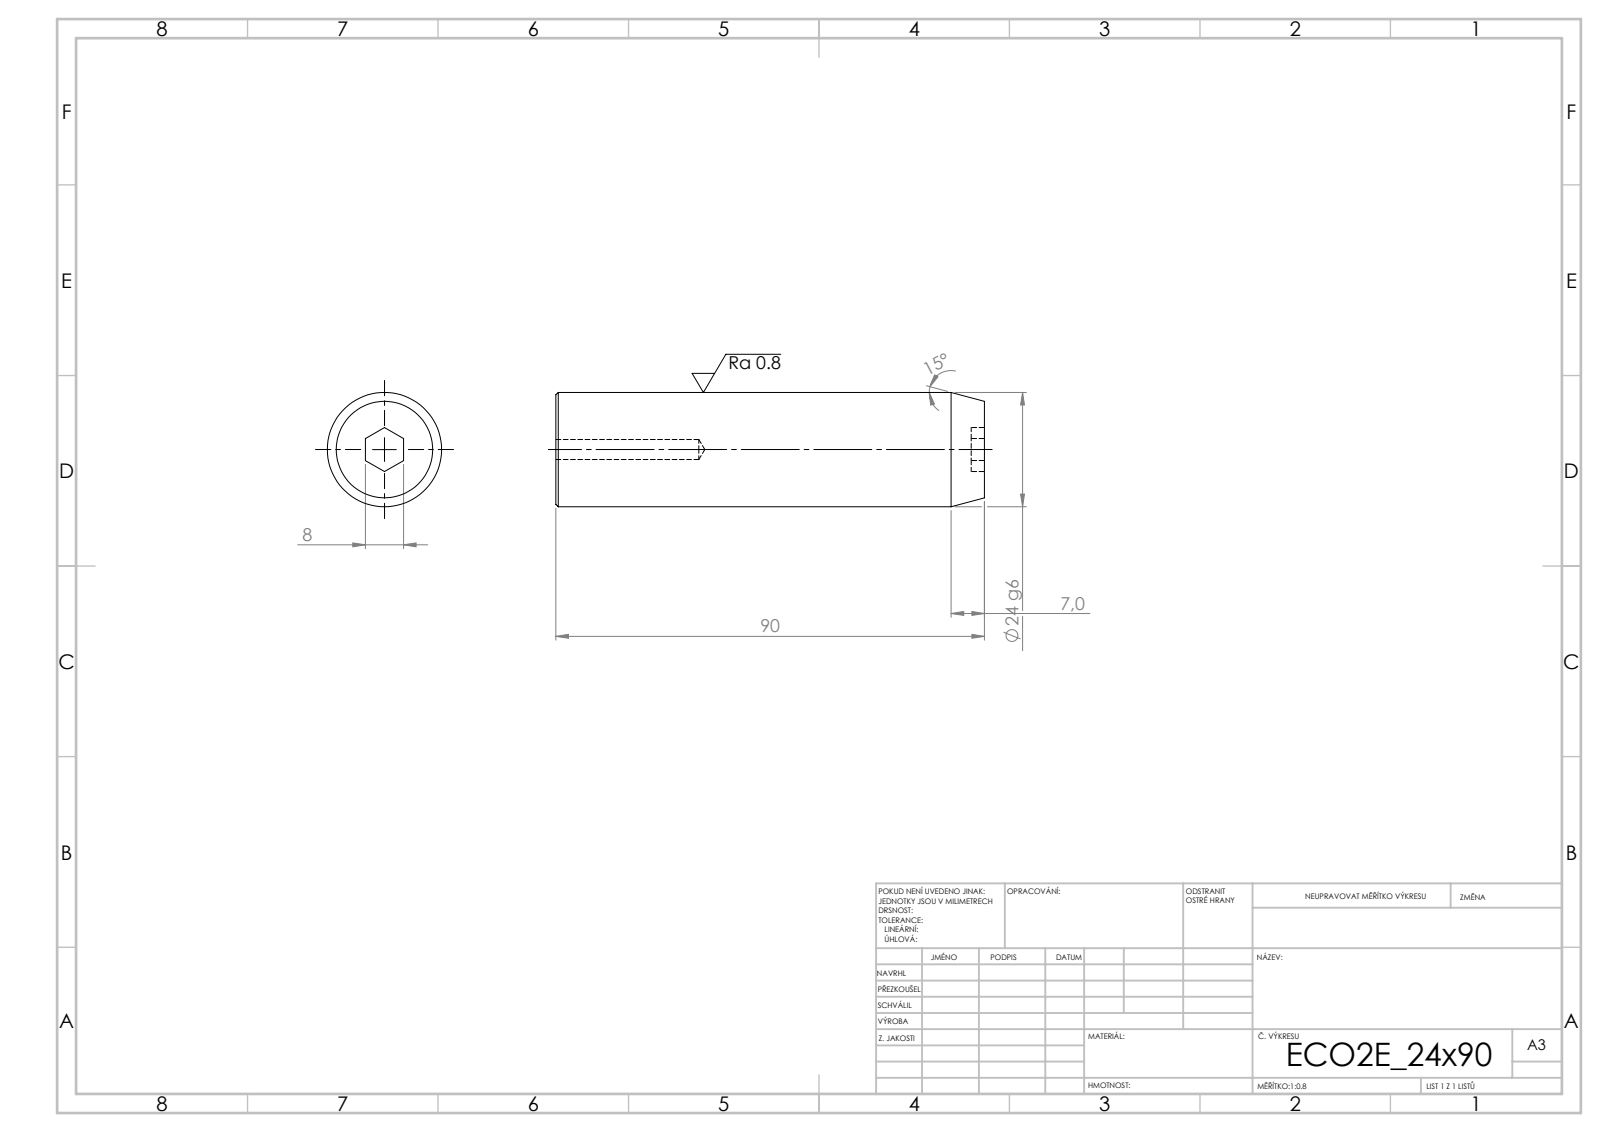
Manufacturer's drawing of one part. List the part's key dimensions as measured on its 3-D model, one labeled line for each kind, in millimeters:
STEP written by: SolidWorks 2019 (CONFIG_CONTROL_DESIGN)
Units: millimetres
Bodies: 1 solid, 19 faces (9 planar, 4 cylindrical, 6 other)
Overall size (bounding box): 90 × 24 × 24
Volume: 39 660 mm³ · Surface area: 7 990 mm²
Round holes (diameter × count): ⌀4.2 ×1
Round bosses / shafts (diameter × count): ⌀24 ×1
Main face-to-face distances: 90, 2.8, 87.2, 8
